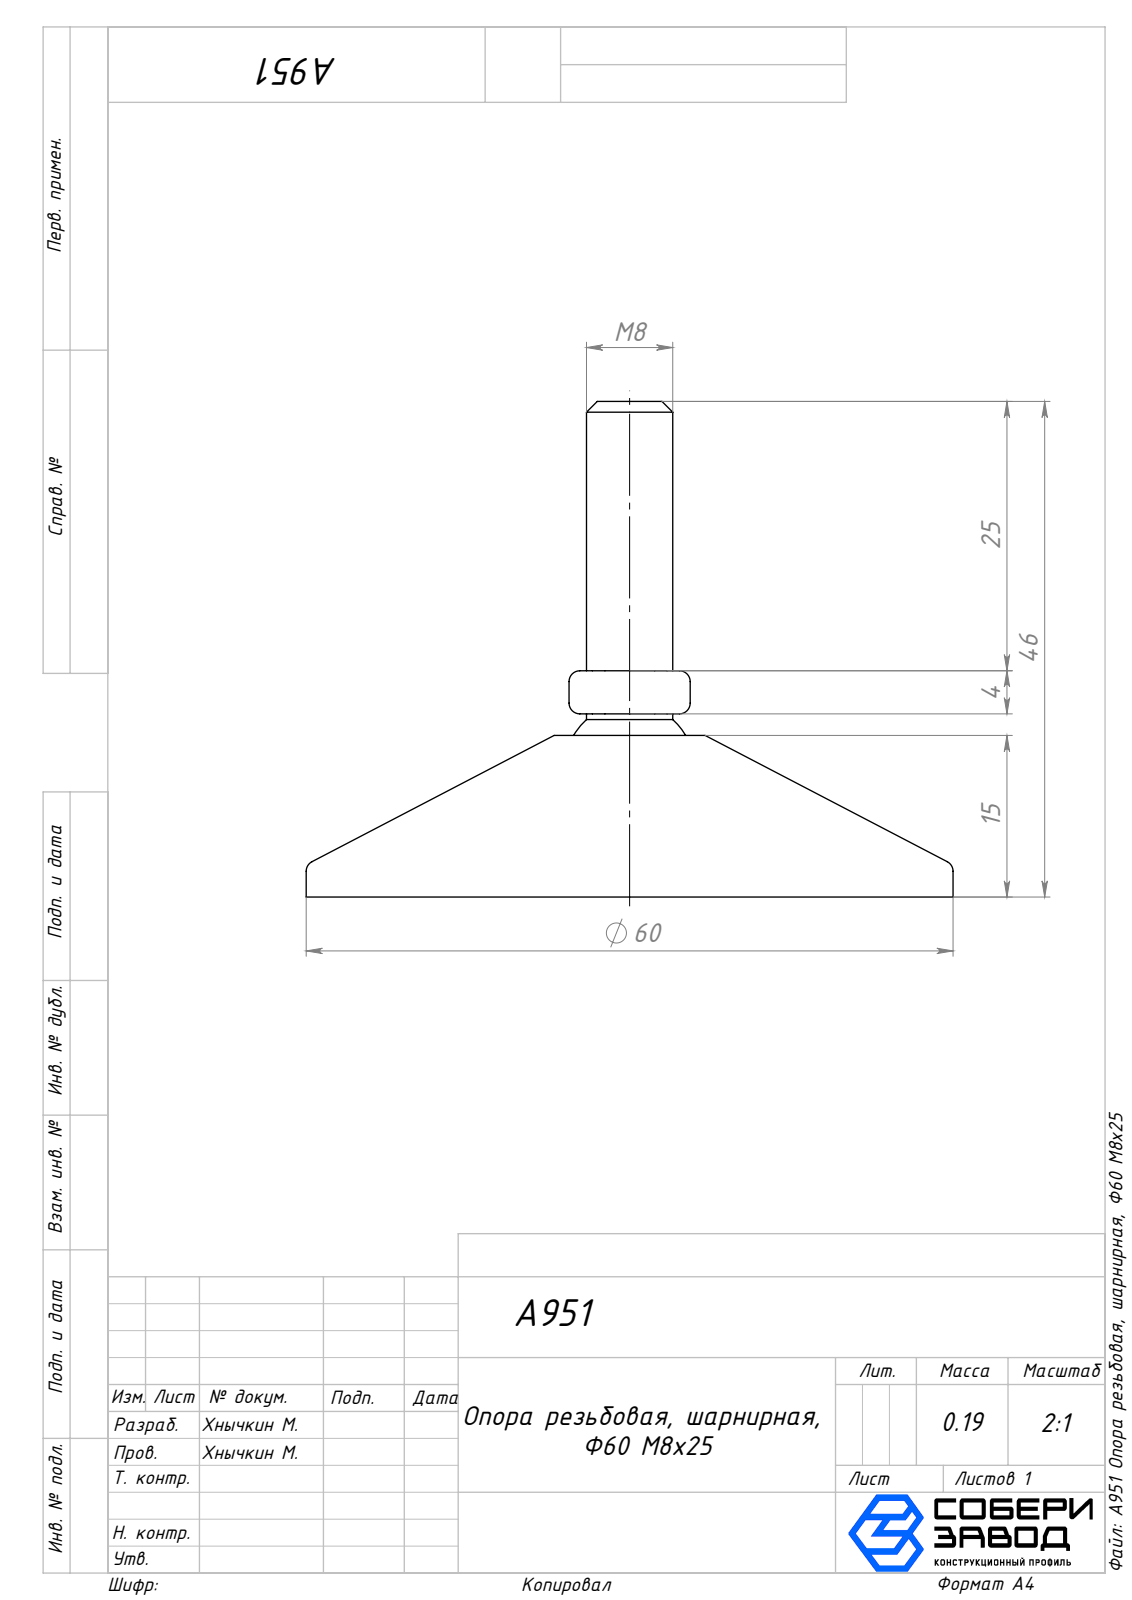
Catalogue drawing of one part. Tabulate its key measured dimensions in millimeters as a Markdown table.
| quantity | value |
| --- | --- |
| part name | A951 Опора Ф60 М8х25_00; A951 Резьба_00; A951 Опора резьбовая, шарнирная, Ф60 М8х25 |
| STEP written by | SolidWorks 2025 (AUTOMOTIVE_DESIGN) |
| units | millimeters |
| bodies | 2 solids, 67 faces (21 planar, 24 cylindrical, 22 other) |
| overall size | 60 × 60 × 46 |
| volume | 24 739 mm³ |
| surface area | 8 042 mm² |
| round bosses / shafts (diameter × count) | 60 × 1, 8 × 1 |
| partial cylindrical surfaces (radius × count) | 1 × 18 |
| main face-to-face distances | 15, 46, 31, 10, 21, 6, 25, 17, 2, 4 |
